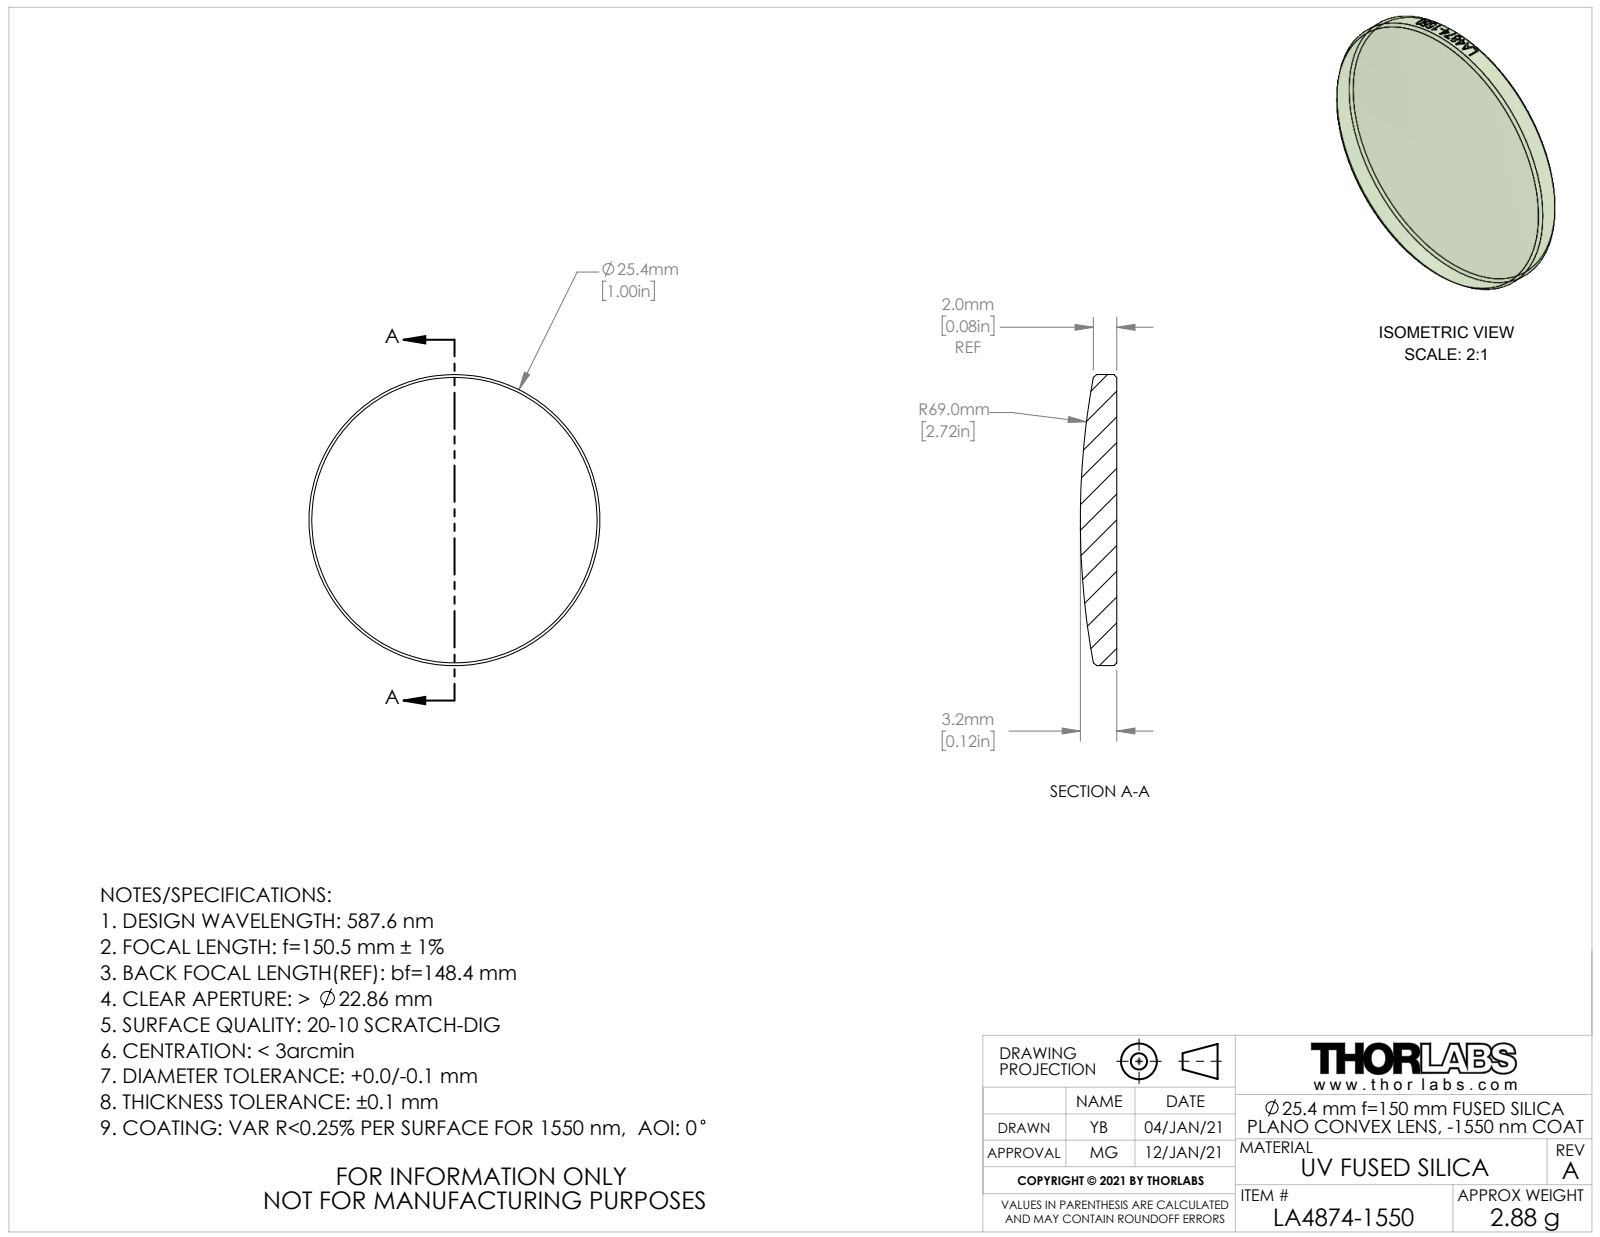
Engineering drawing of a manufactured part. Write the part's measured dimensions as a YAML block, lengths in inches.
part_name: "CTN015942-E0W"
step_written_by: "SolidWorks 2018 (AUTOMOTIVE_DESIGN)"
units: inches
bodies: {solids: 1, faces: 28, planar: 1, cylindrical: 21, other: 6}
overall_size: [1, 1, 0.125]
volume: 0.08
surface_area: 1.792
round_bosses_or_shafts:
  - {diameter: 1, count: 1}
